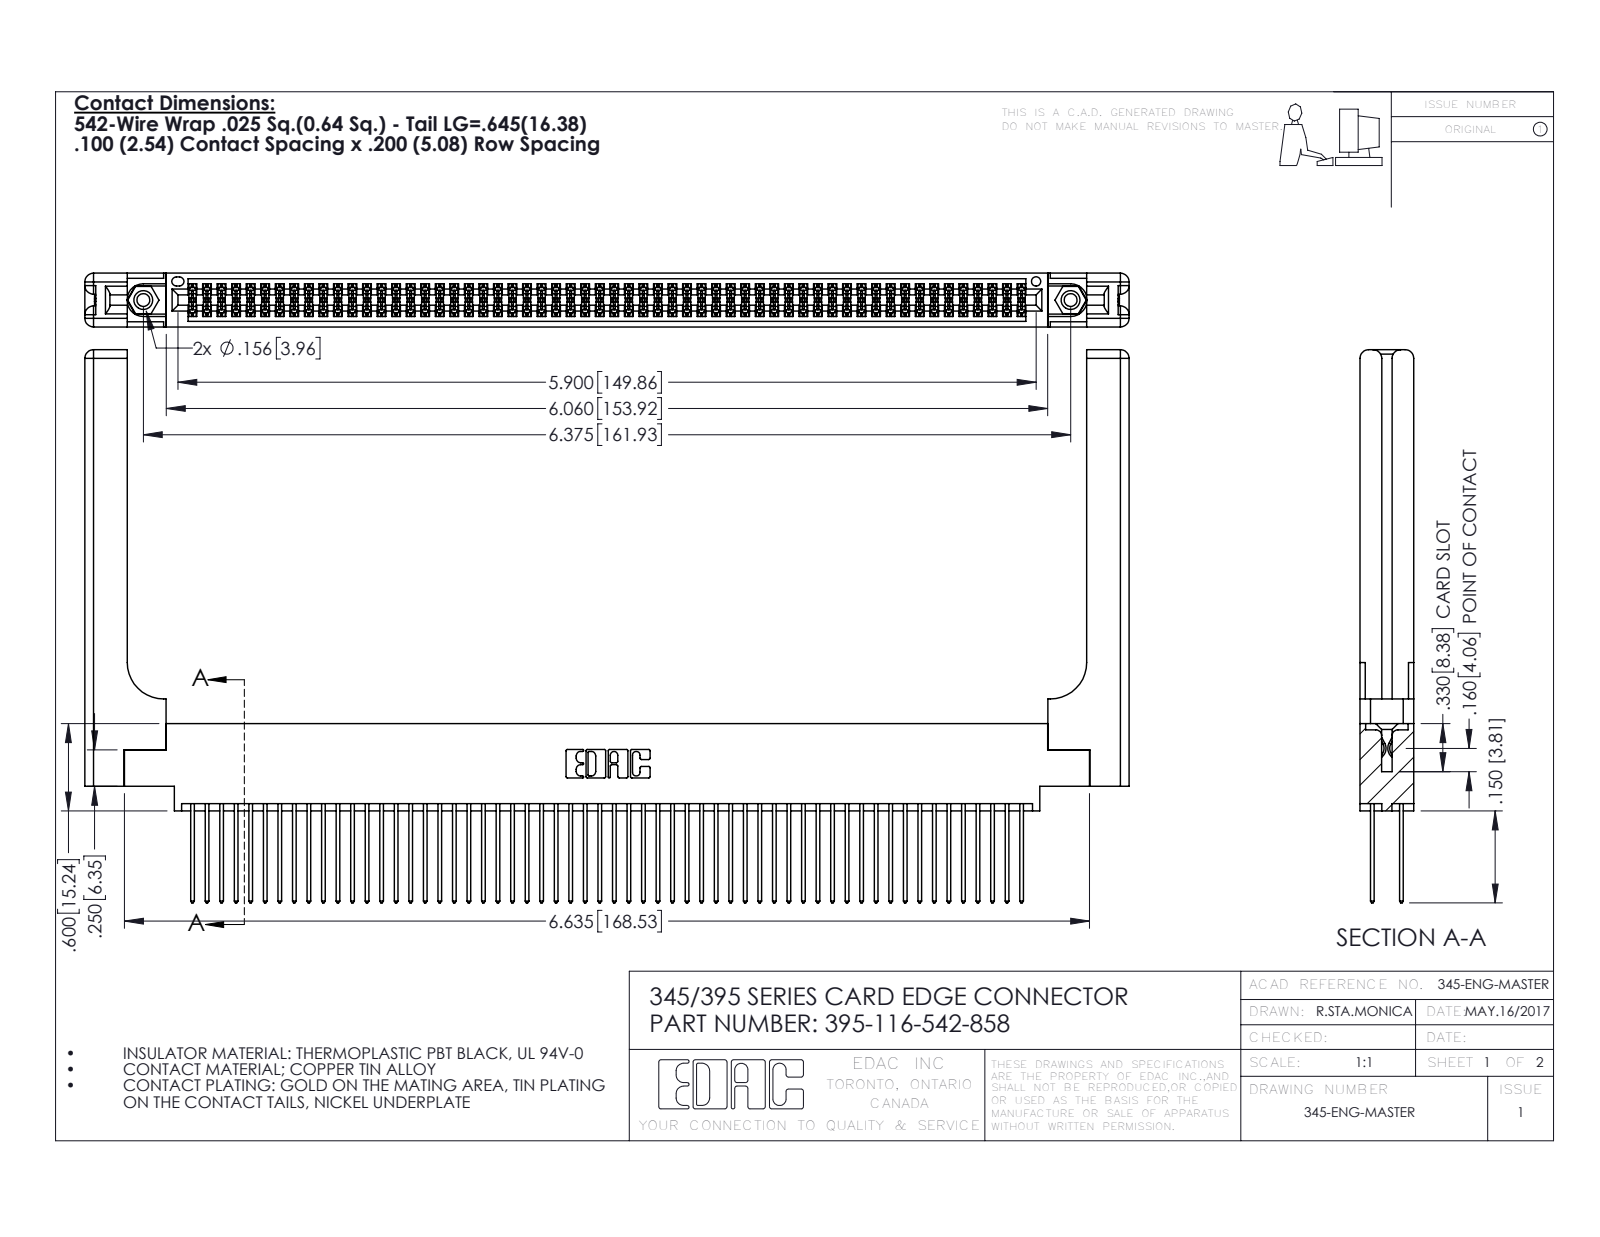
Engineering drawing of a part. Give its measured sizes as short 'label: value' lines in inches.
name: 345-250-001_345-250-001-102; 345-220-058_345-220-058; 395-116-542-858; 345-292-001_345-293-142 (+1 more)
written by: SolidWorks 2016 (CONFIG_CONTROL_DESIGN)
unit: in
bodies: 121 solids, 6186 faces (4060 planar, 2066 cylindrical, 60 other)
size: 7.179 × 3.802 × 0.37
volume: 1.633 in³; area: 54.36 in²
holes: 2× ⌀0.089, 2× ⌀0.125, 2× ⌀0.156, 1× ⌀0.064
bosses: 2× ⌀0.155
rounds: 174× R0.006, 116× R0.01, 22× R0.01, 16× R0.06, 6× R0.007, 6× R0.031, 3× R0.026, 2× R0.014
face distances: 0.072, 0.298, 0.37, 0.098, 0.272, 0.025, 0.2, 0.225, 0.175, 0.148
hole spacings: 0.27, 6.139, 6.375
